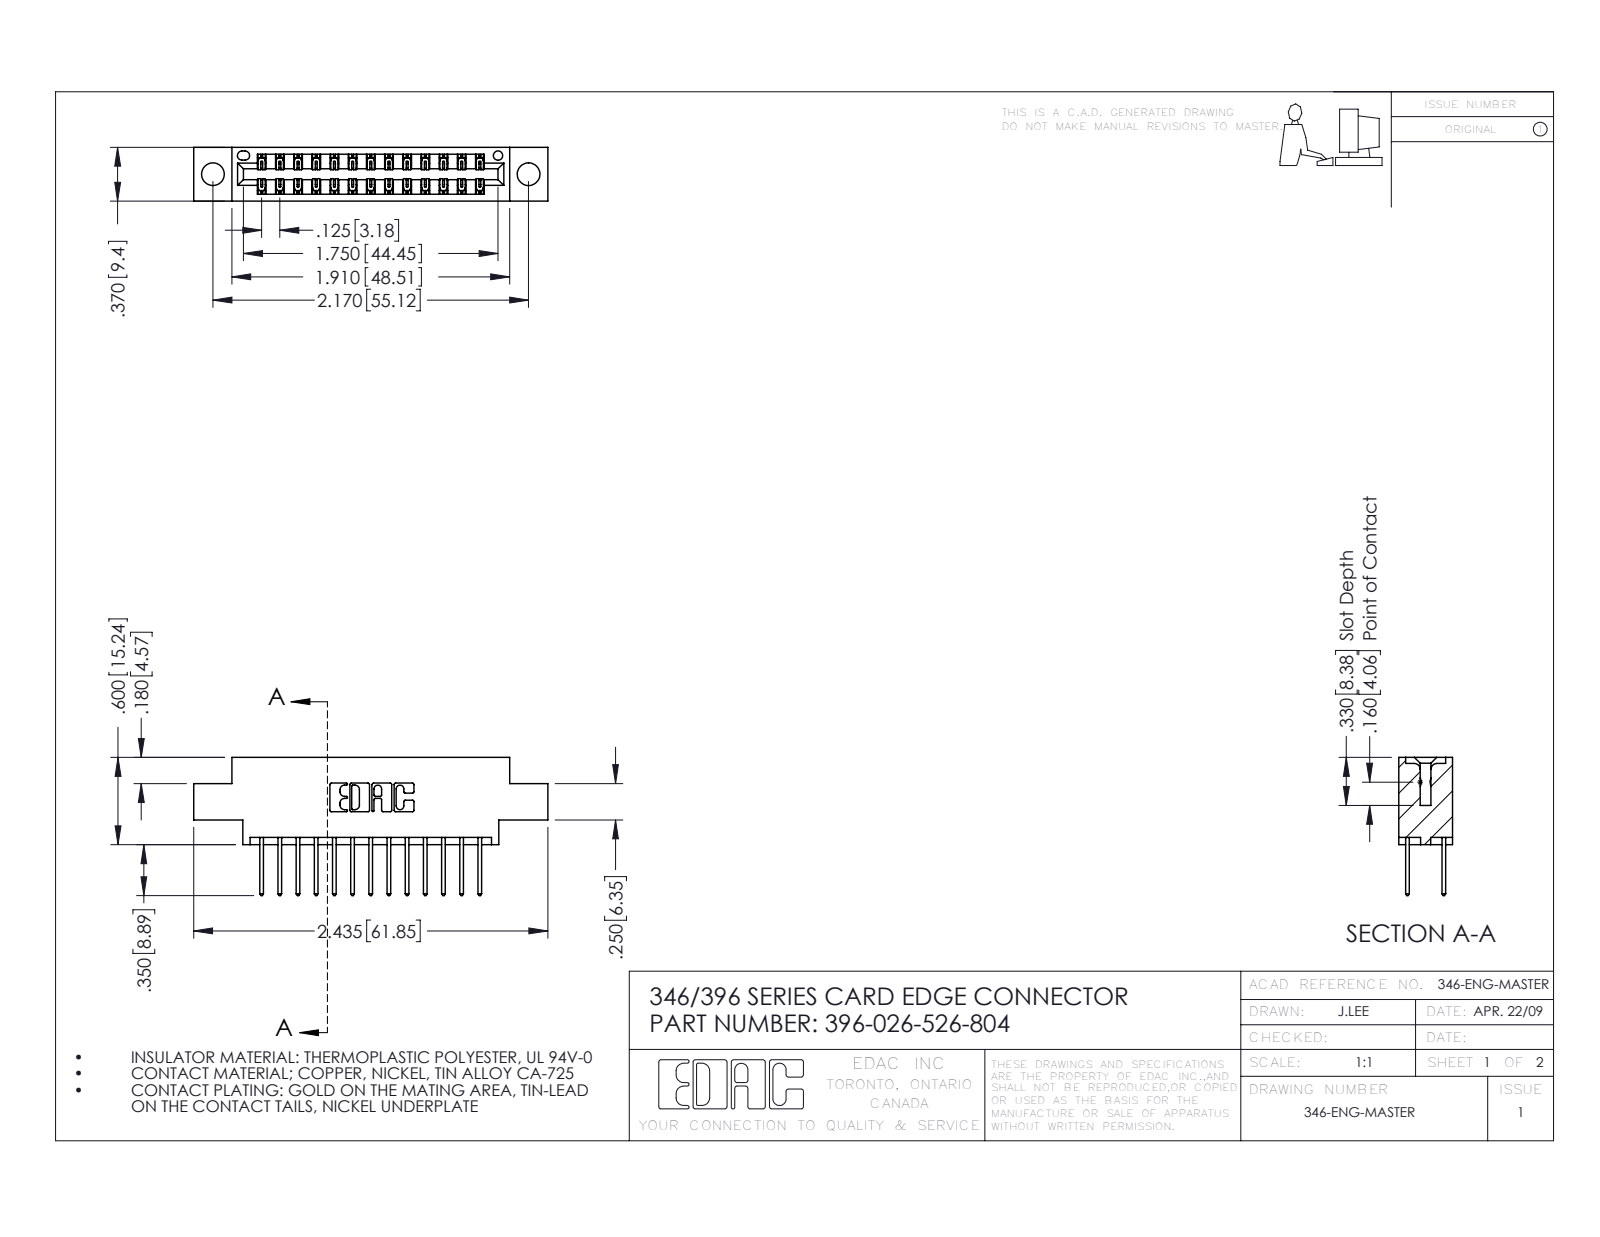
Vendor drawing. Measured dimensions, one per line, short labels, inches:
name: 396-026-526-804; 346 Part_0.170 Offset - 0.156 Dia-TH; 345-292-001_345-293-126
written by: SolidWorks 2016 (CONFIG_CONTROL_DESIGN)
unit: in
bodies: 27 solids, 1478 faces (990 planar, 488 cylindrical, 0 other)
size: 2.435 × 0.95 × 0.37
volume: 0.342 in³; area: 11.52 in²
holes: 2× ⌀0.156, 1× ⌀0.064
rounds: 39× R0.006, 26× R0.01, 22× R0.01, 6× R0.007, 6× R0.031, 3× R0.026, 2× R0.014, 2× R0.022
face distances: 0.048, 0.322, 0.25, 0.37, 0.072, 0.298, 0.025, 0.275, 0.148, 0.222
hole spacings: 0.246, 1.964, 2.17
